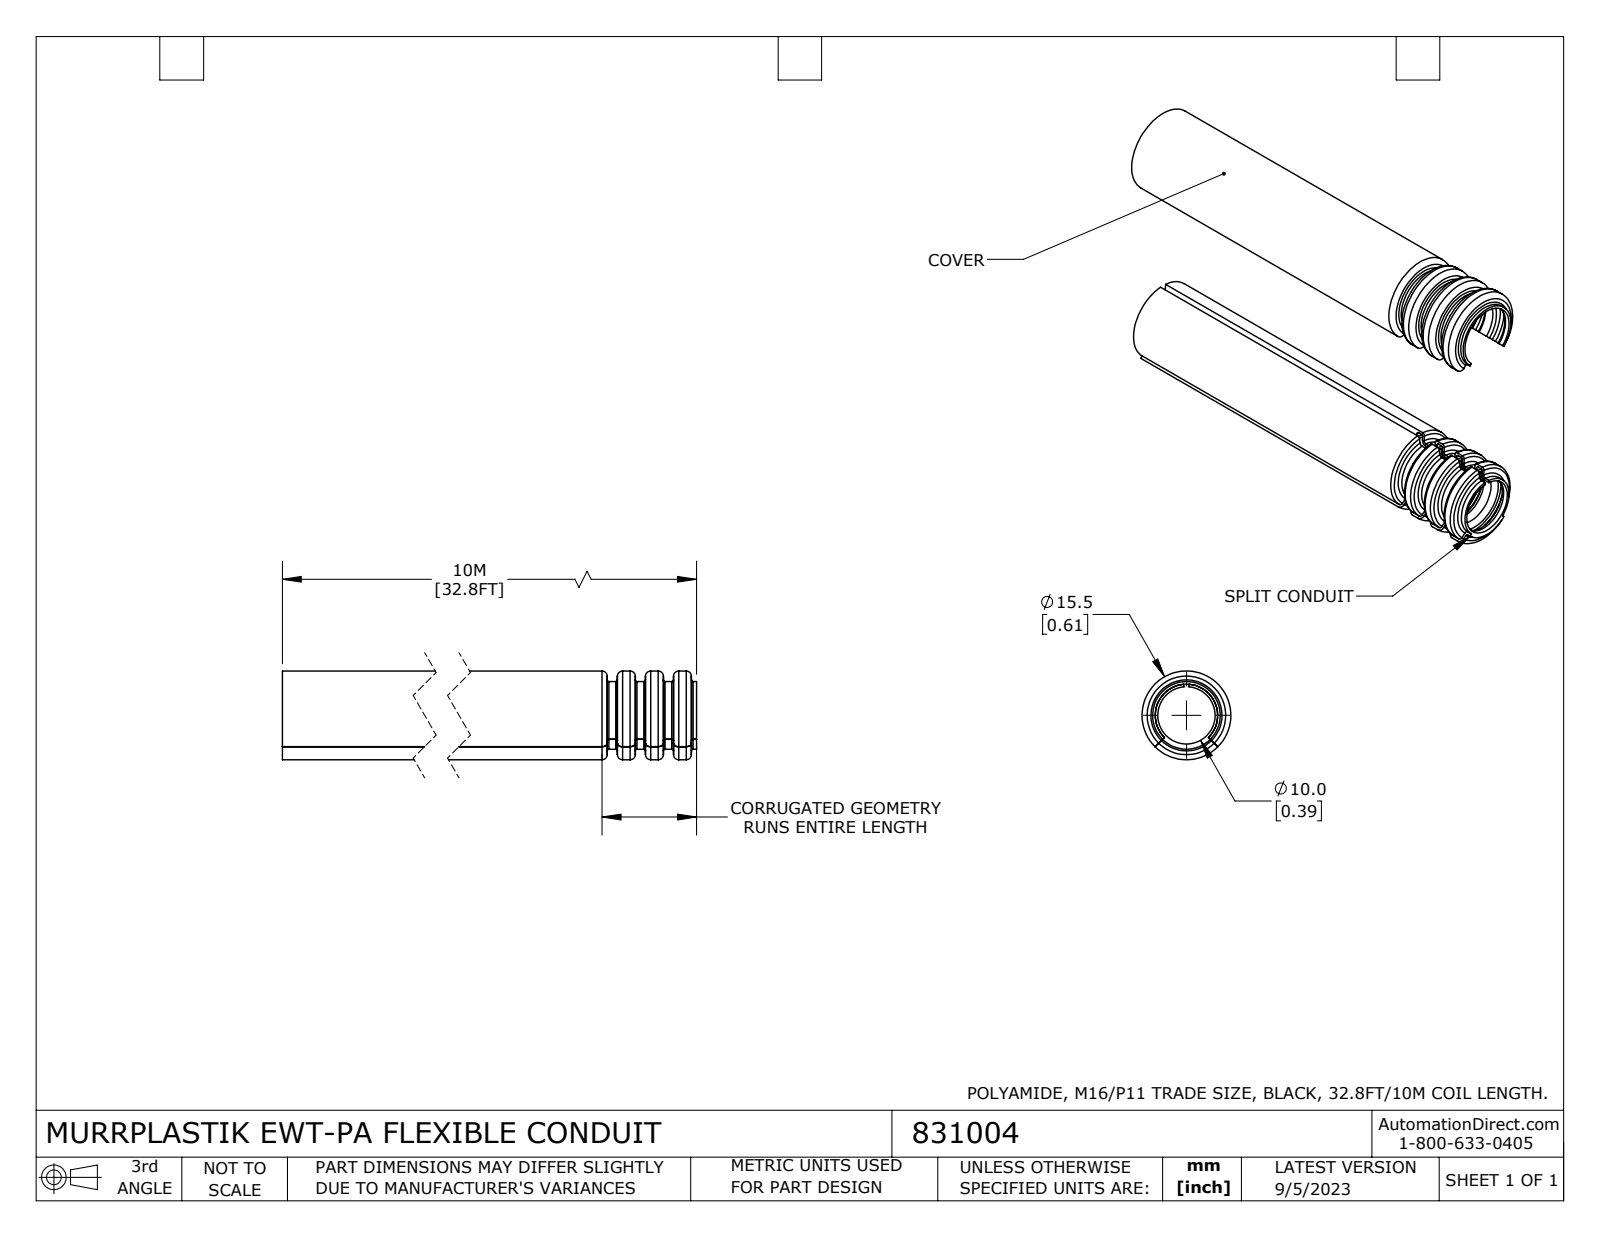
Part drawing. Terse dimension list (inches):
name: 831004
written by: SolidWorks 2021 (CONFIG_CONTROL_DESIGN)
unit: in
bodies: 2 solids, 339 faces (10 planar, 107 cylindrical, 222 other)
size: 3.15 × 0.61 × 0.61
volume: 0.469 in³; area: 21.02 in²
holes: 1× ⌀0.394, 1× ⌀0.539
bosses: 1× ⌀0.61, 1× ⌀0.465
rounds: 1× R0.215, 1× R0.287
face distances: 3.15
